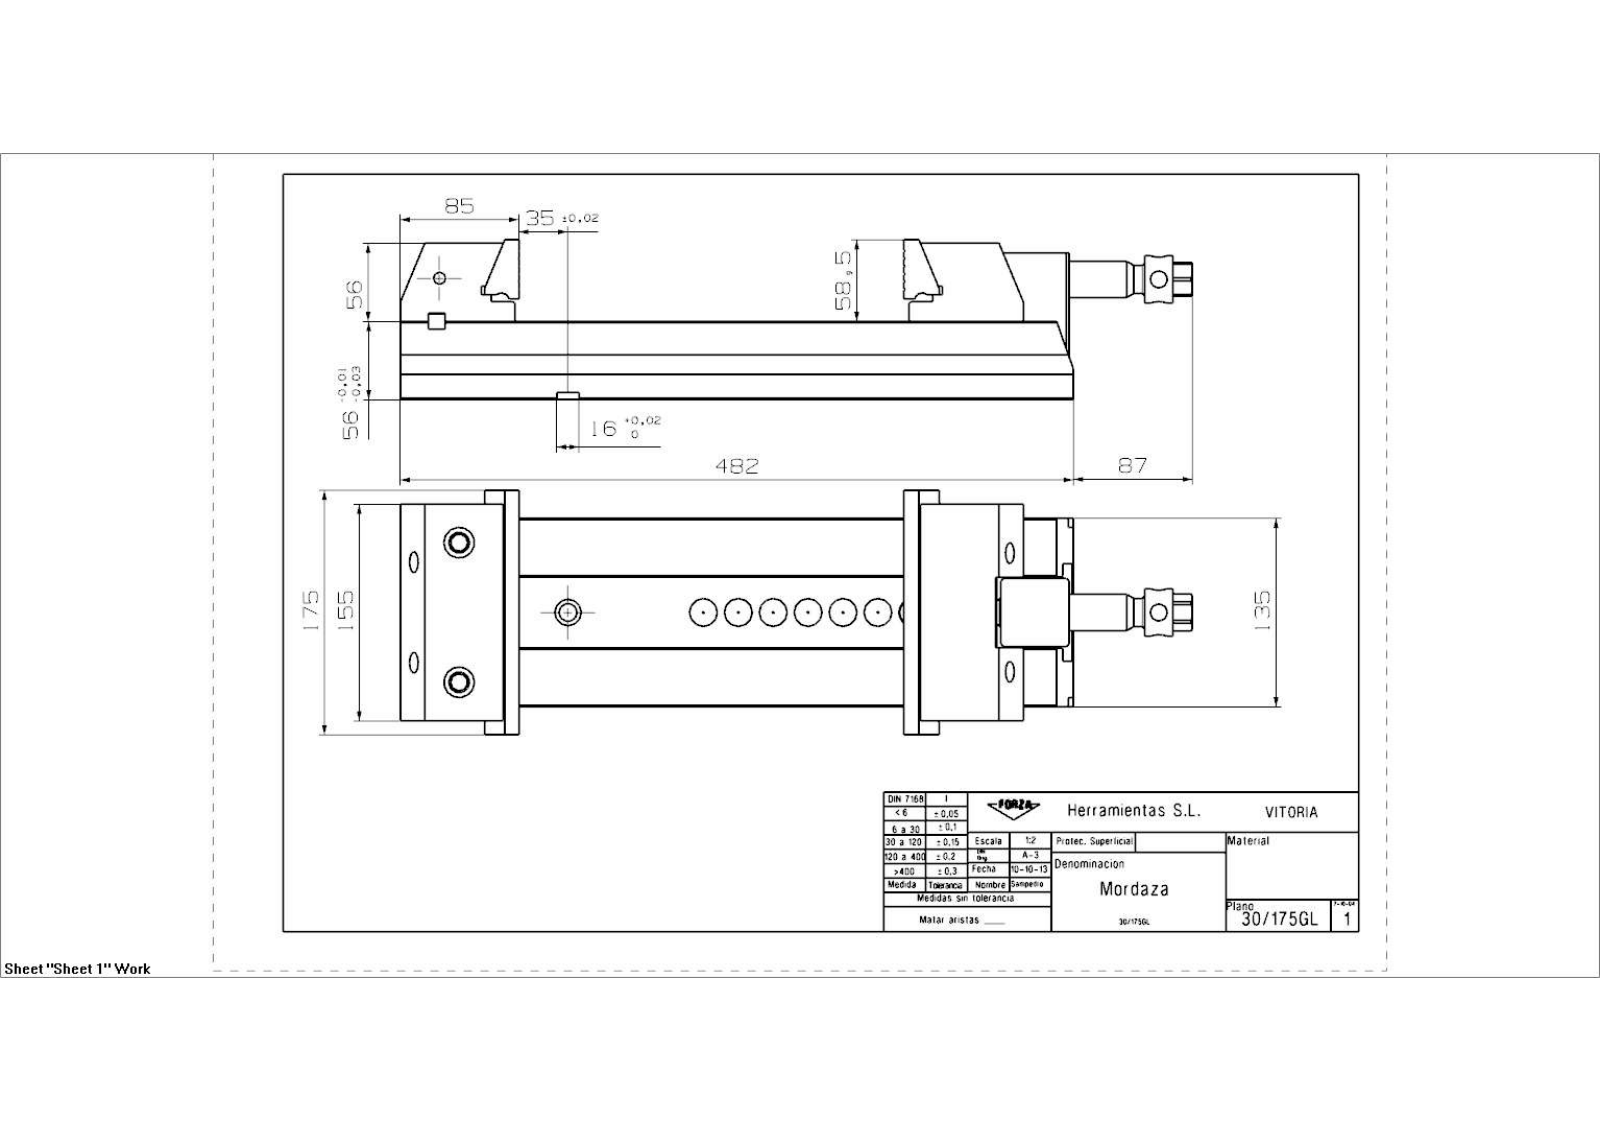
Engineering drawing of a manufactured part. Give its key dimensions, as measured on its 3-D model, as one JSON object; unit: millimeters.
{"part_name": "30_175GL_Mordaza", "step_written_by": "SIEMENS PLM Software NX 7.5 (AUTOMOTIVE_DESIGN)", "units": "millimeters", "bodies": {"solids": 12, "faces": 469, "planar": 309, "cylindrical": 97, "other": 63}, "overall_size": [567.23, 175, 114], "volume_mm3": 4075000, "surface_area_mm2": 518816, "round_holes": [[13, 6], [15, 6], [19, 6], [5.19, 5], [6.99, 4], [8.5, 4], [10.58, 4], [8.78, 3], [9.5, 2], [10, 2], [12, 2], [12.38, 2]], "round_bosses_or_shafts": [[34, 1], [33.8, 1], [26, 1], [20, 1], [16.5, 1]], "partial_cylinders_radius": [[20, 4], [1.6, 2], [6, 2], [7, 2], [7.75, 2], [8, 2], [4, 1], [9, 1]], "face_to_face_distances": [56, 24.2, 31.8, 135, 32.5, 102.5, 56.25, 96, 10, 112.25], "hole_center_spacings": [6.5, 78.5, 72, 85, 106.07, 100, 27.76, 27.78]}
